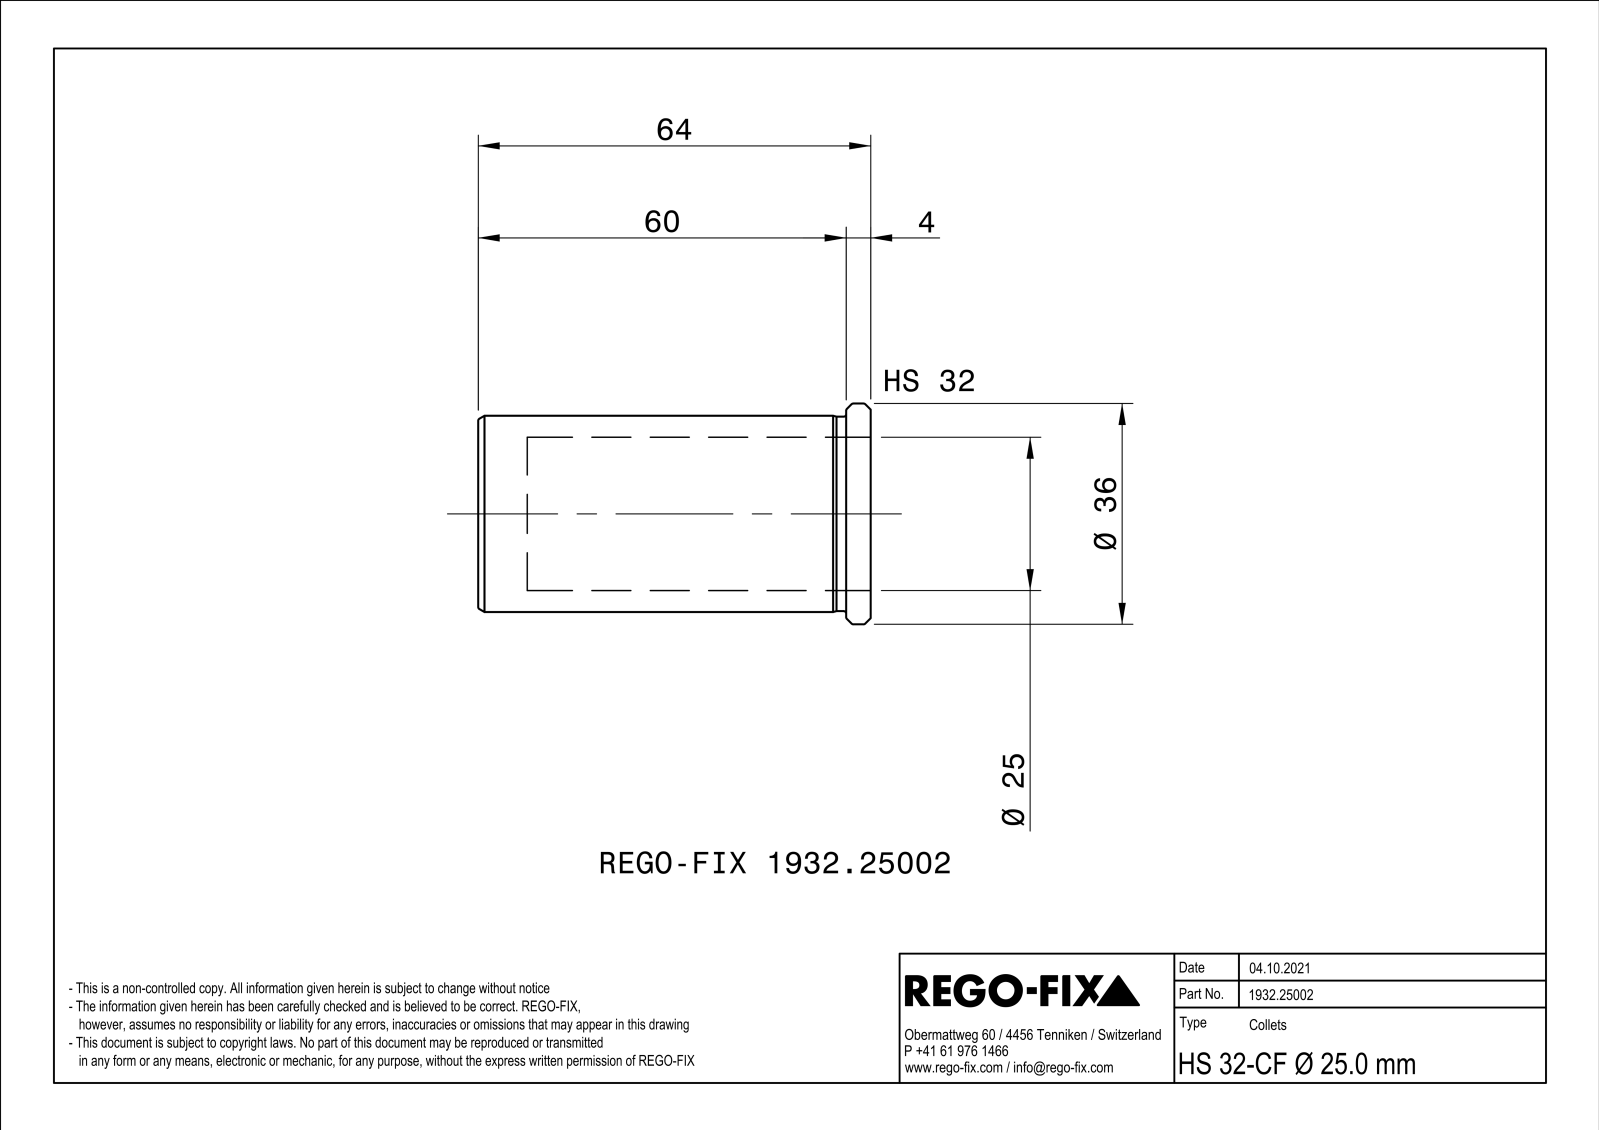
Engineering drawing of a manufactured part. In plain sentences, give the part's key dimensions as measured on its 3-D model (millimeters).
The part is named "NOCUT". Its 3-D file was written by "SIEMENS PLM Software Solid Edge ST10 (AUTOMOTIVE_DESIGN)". It is 1 solid with 83 faces: 14 planar, 26 cylindrical and 43 other. Overall it measures 64 by 35.99 by 35.99 millimeters. Its volume is 19 353 cubic millimeters and its surface area 13 604 square millimeters. Round holes: 1 of diameter 25, 1 of diameter 26.5. Round bosses or shafts: 1 of diameter 36, 1 of diameter 32, 1 of diameter 31.7. Partial cylindrical surfaces (rounded edges, fillets, slot ends): 6 of radius 0.5, 4 of radius 0.75. The main face-to-face distances are 1, 64, 4, 60.
